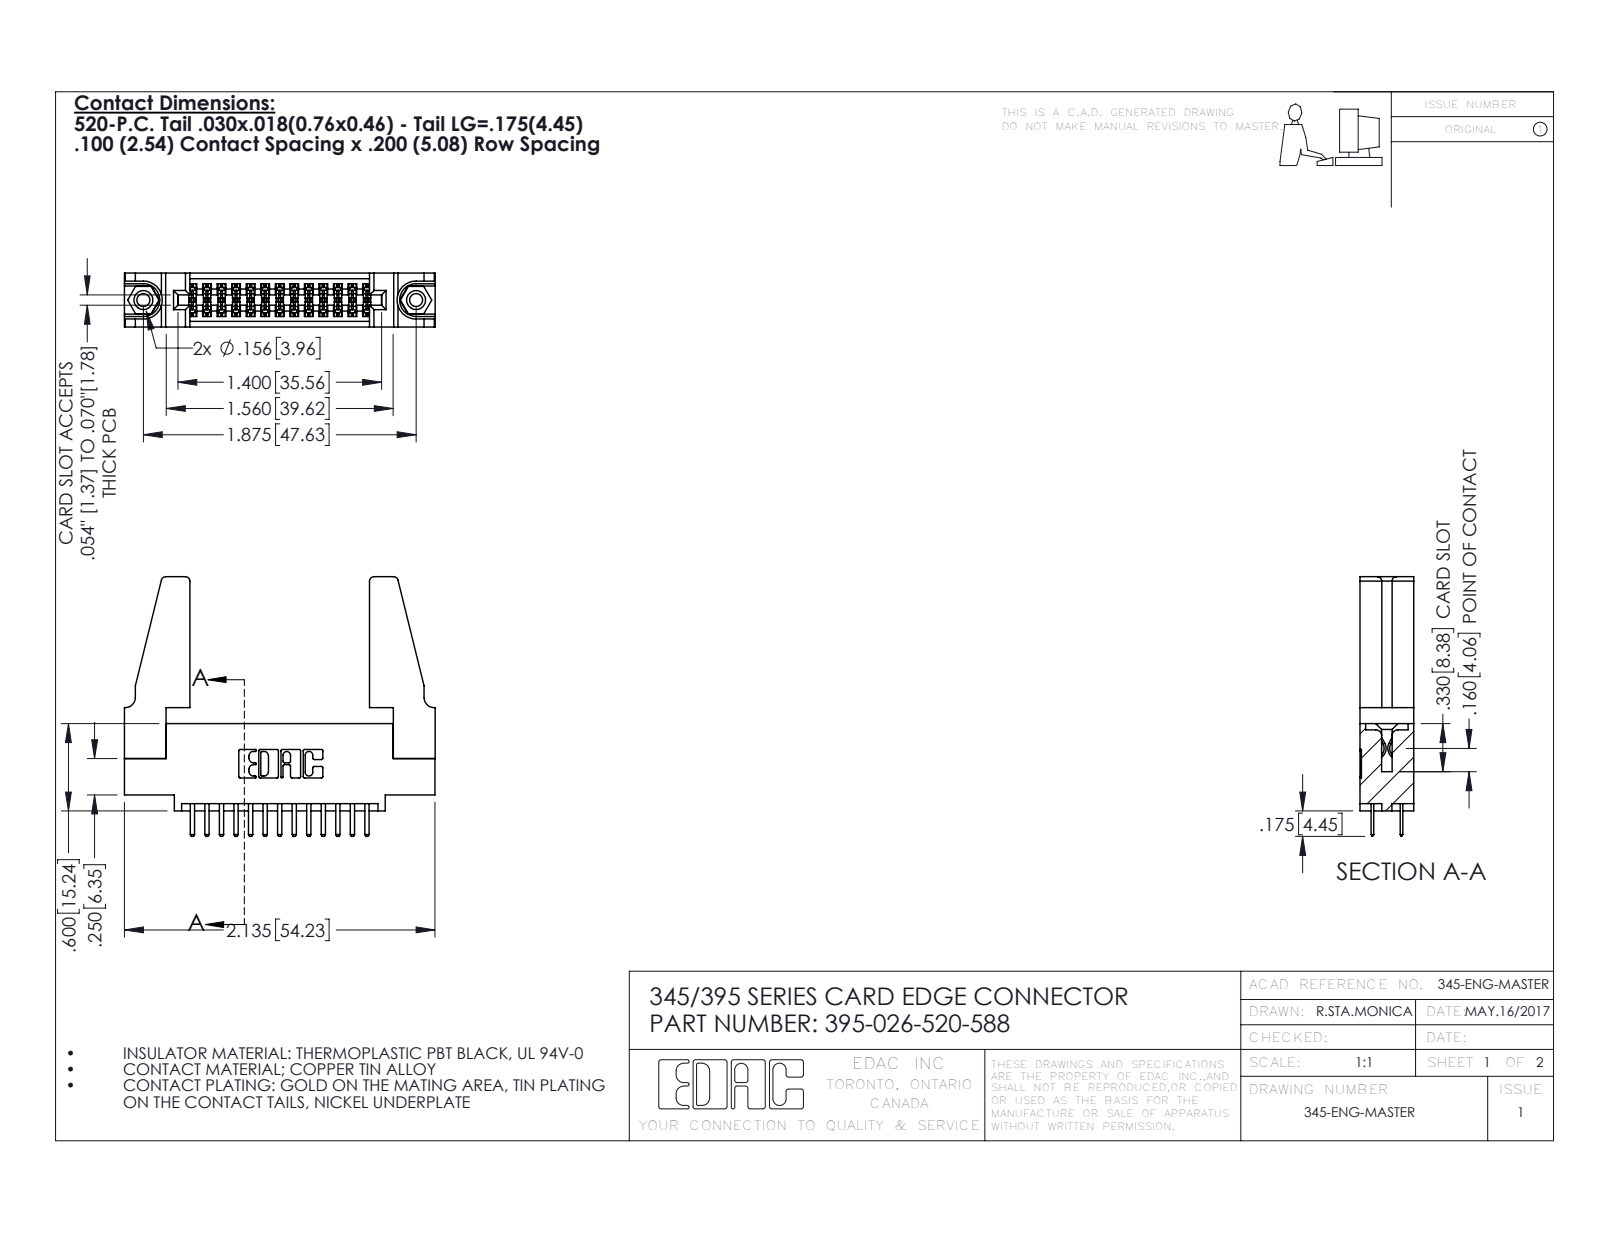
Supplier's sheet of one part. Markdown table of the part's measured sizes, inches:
| quantity | value |
| --- | --- |
| part name | 345-250-001_345-250-001-102; 345-220-078_345-220-088; 395-026-520-588; 345-292-001_345-293-120 (+1 more) |
| STEP written by | SolidWorks 2016 (CONFIG_CONTROL_DESIGN) |
| units | inches |
| bodies | 31 solids, 1658 faces (1066 planar, 576 cylindrical, 16 other) |
| overall size | 2.136 × 1.785 × 0.37 |
| volume | 0.498 in³ |
| surface area | 15.34 in² |
| round holes (diameter × count) | 0.089 × 2, 0.125 × 2, 0.156 × 2, 0.064 × 1 |
| round bosses / shafts (diameter × count) | 0.155 × 2 |
| partial cylindrical surfaces (radius × count) | 0.006 × 39, 0.01 × 30, 0.01 × 22, 0.03 × 8, 0.007 × 6, 0.031 × 6, 0.026 × 3, 0.014 × 2 |
| main face-to-face distances | 0.37, 0.072, 0.298, 0.2, 0.098, 0.272, 0.025, 0.225, 0.022, 0.31 |
| hole center spacings | 0.27, 1.643, 1.875 |
